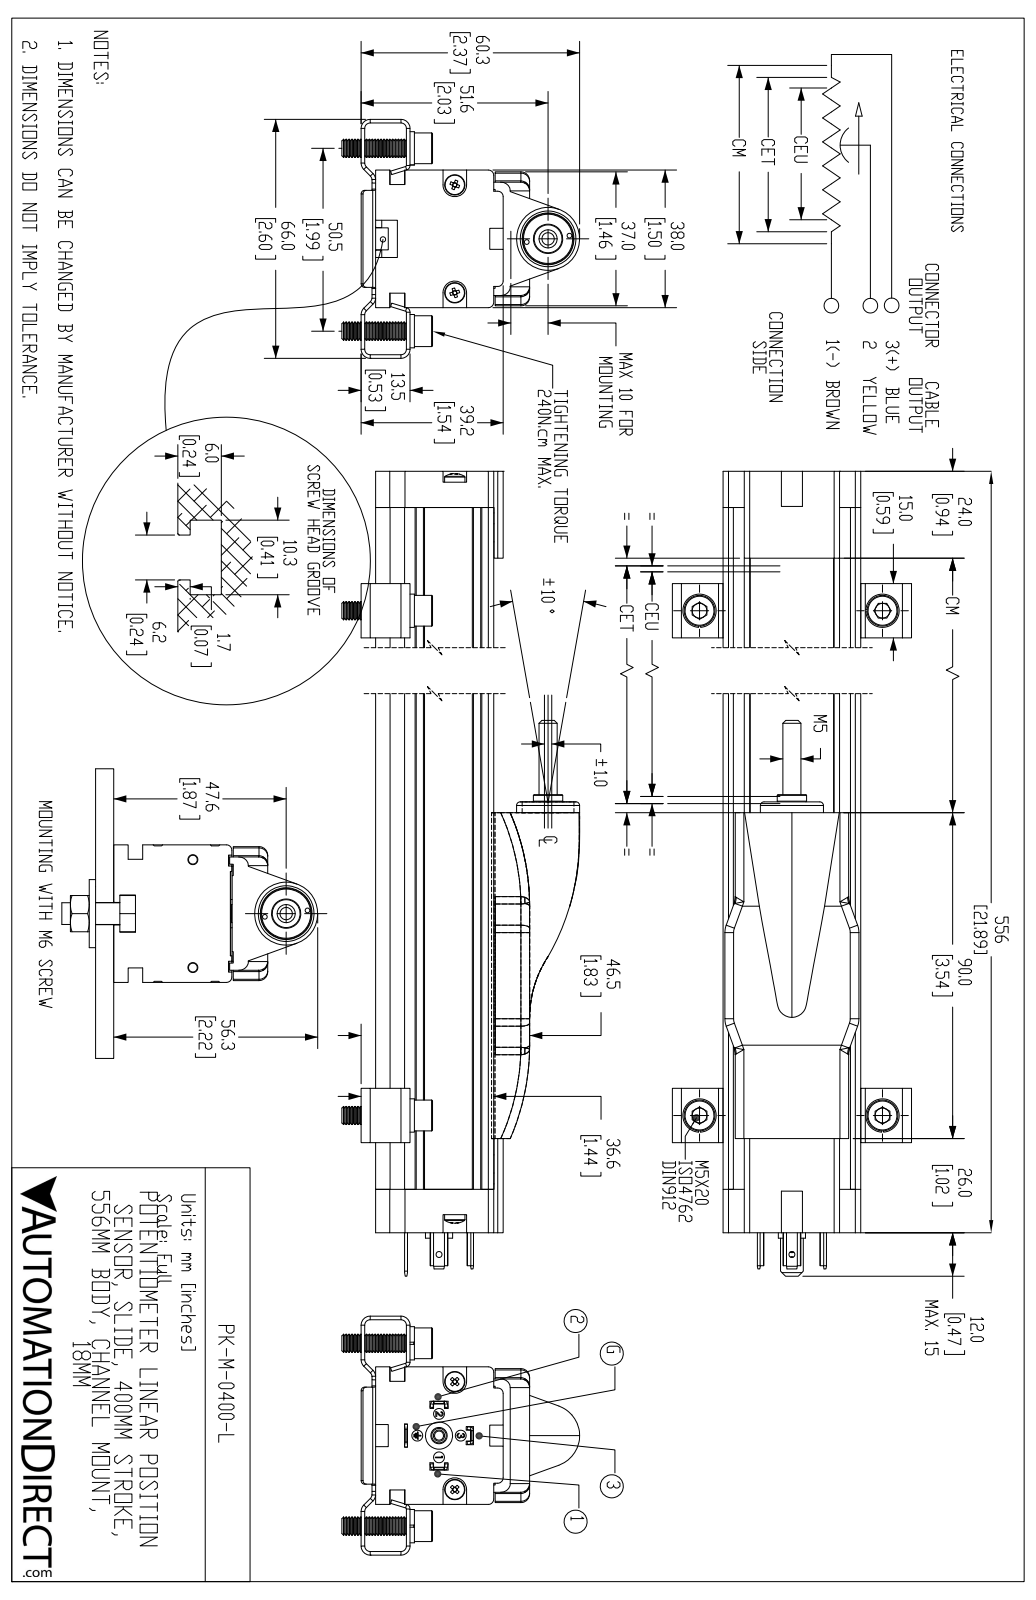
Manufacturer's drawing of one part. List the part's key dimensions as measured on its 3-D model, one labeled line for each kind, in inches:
Part name (STEP PRODUCT): PK-M-0400-L
STEP written by: SolidWorks 2019 (AUTOMOTIVE_DESIGN)
Units: inches
Bodies: 27 solids, 1761 faces (785 planar, 384 cylindrical, 592 other)
Overall size (bounding box): 22.362 × 2.598 × 2.583
Volume: 40.81 in³ · Surface area: 261.2 in²
Round holes (diameter × count): ⌀0.118 ×5, ⌀0.201 ×4, ⌀0.051 ×2, ⌀0.059 ×2, ⌀0.065 ×2, ⌀0.102 ×2, ⌀0.108 ×2, ⌀0.13 ×2, ⌀0.209 ×2, ⌀0.063 ×1, ⌀0.098 ×1, ⌀0.157 ×1
Round bosses / shafts (diameter × count): ⌀0.197 ×7, ⌀0.362 ×4, ⌀0.335 ×4, ⌀0.22 ×2, ⌀0.118 ×2, ⌀0.098 ×2, ⌀0.685 ×1, ⌀0.551 ×1
Partial cylindrical surfaces — rounded edges, fillets, slot ends (radius × count): R0.039 ×28, R0.059 ×12, R0.098 ×8, R0.104 ×8, R0.236 ×8, R0.033 ×6, R0.094 ×6, R0.024 ×4
Main face-to-face distances: 1.268, 0.157, 1.272, 1.496, 0.079, 0.039, 0.02, 0.016, 1.035, 0.315
Hole centre spacings: 0.236, 0.334, 0.234, 0.39, 0.472, 0.484, 0.539, 0.59
